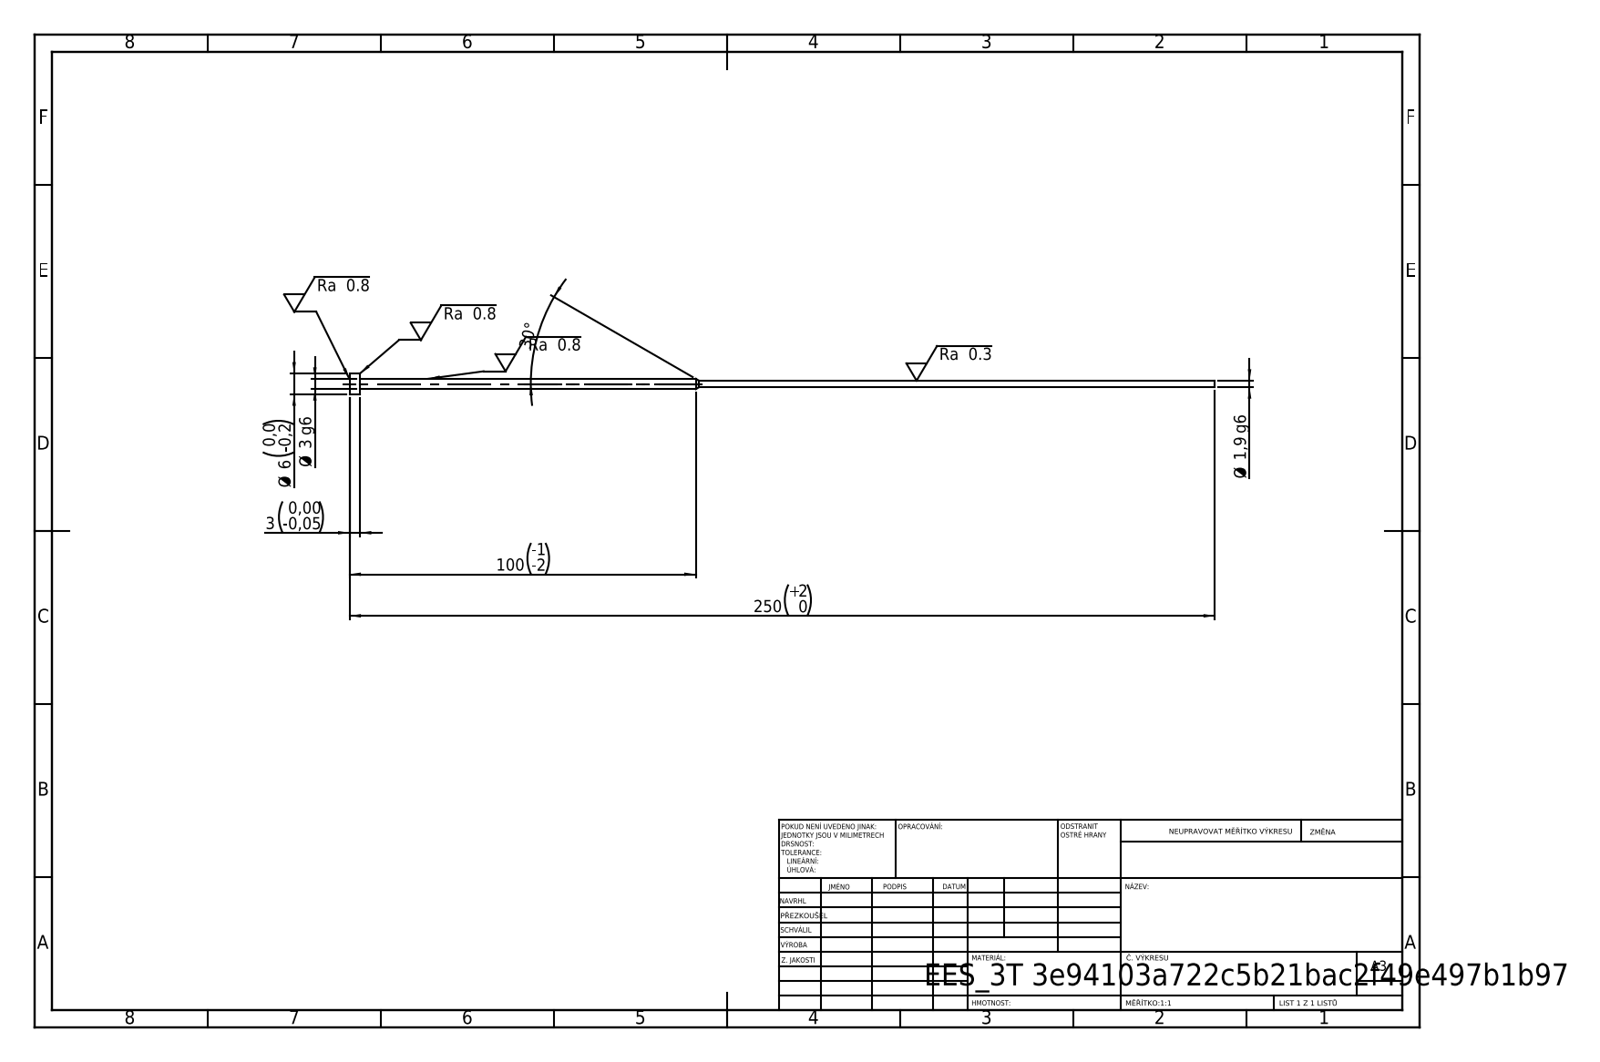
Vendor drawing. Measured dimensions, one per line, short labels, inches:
written by: SolidWorks 2019 (CONFIG_CONTROL_DESIGN)
unit: in
bodies: 1 solid, 11 faces (3 planar, 6 cylindrical, 2 other)
size: 9.843 × 0.236 × 0.236
volume: 0.073 in³; area: 2.978 in²
bosses: 1× ⌀0.236, 1× ⌀0.118, 1× ⌀0.075
face distances: 0.118, 9.724, 9.843
